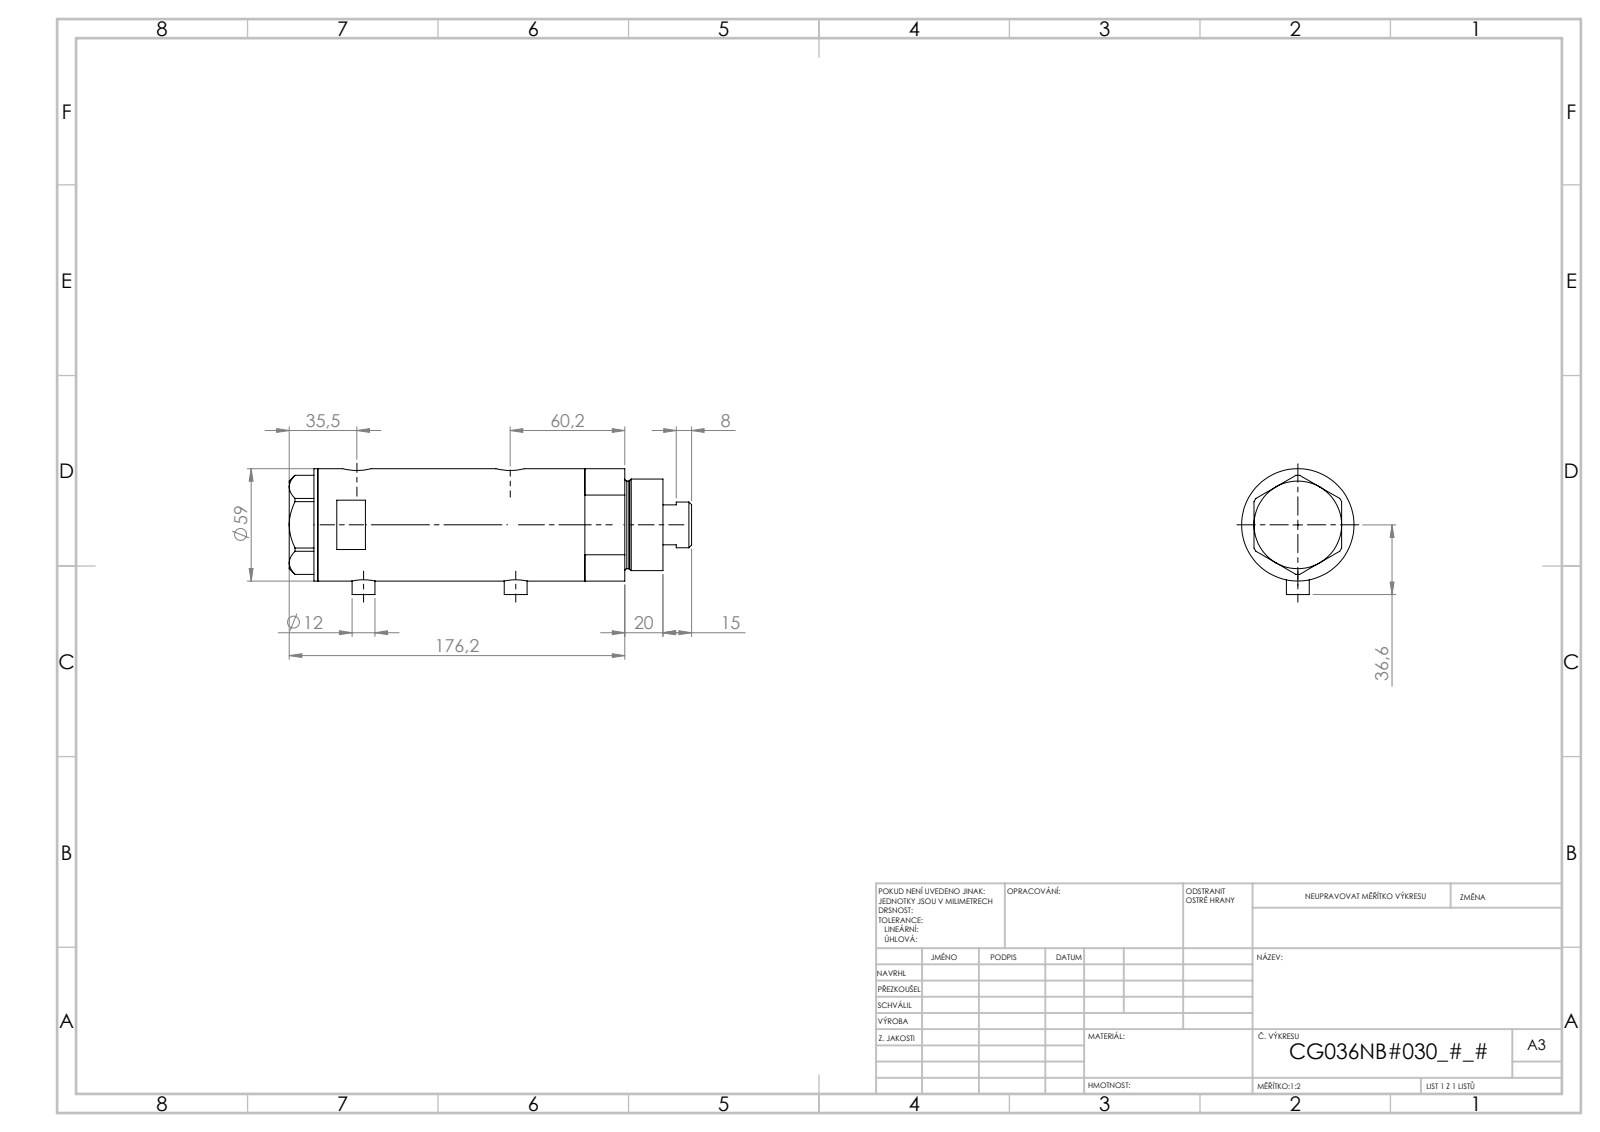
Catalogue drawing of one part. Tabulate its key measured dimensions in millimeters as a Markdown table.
| quantity | value |
| --- | --- |
| part name | V270CG_MIDDLE; V270CG_FRONT; V270CG_VC; V270CG_BACK |
| STEP written by | SolidWorks 2019 (CONFIG_CONTROL_DESIGN) |
| units | millimeters |
| bodies | 4 solids, 126 faces (53 planar, 53 cylindrical, 20 other) |
| overall size | 193.42 × 60.1 × 59 |
| volume | 437 351 mm³ |
| surface area | 93 203 mm² |
| round holes (diameter × count) | 5 × 2, 9.73 × 2, 12.5 × 2, 15 × 2, 8.5 × 1, 25 × 1, 26.5 × 1, 36 × 1, 40 × 1, 52 × 1 |
| round bosses / shafts (diameter × count) | 12 × 2, 59 × 1, 48 × 1, 46 × 1, 24 × 1 |
| main face-to-face distances | 87.34, 23.5, 63.84, 15, 38.5, 102.34, 178.42, 163.42, 139.92, 76.08 |
| hole center spacings | 2.9, 3.5, 62.15, 65.05, 65.65, 68.55, 2.89, 2.91 |
